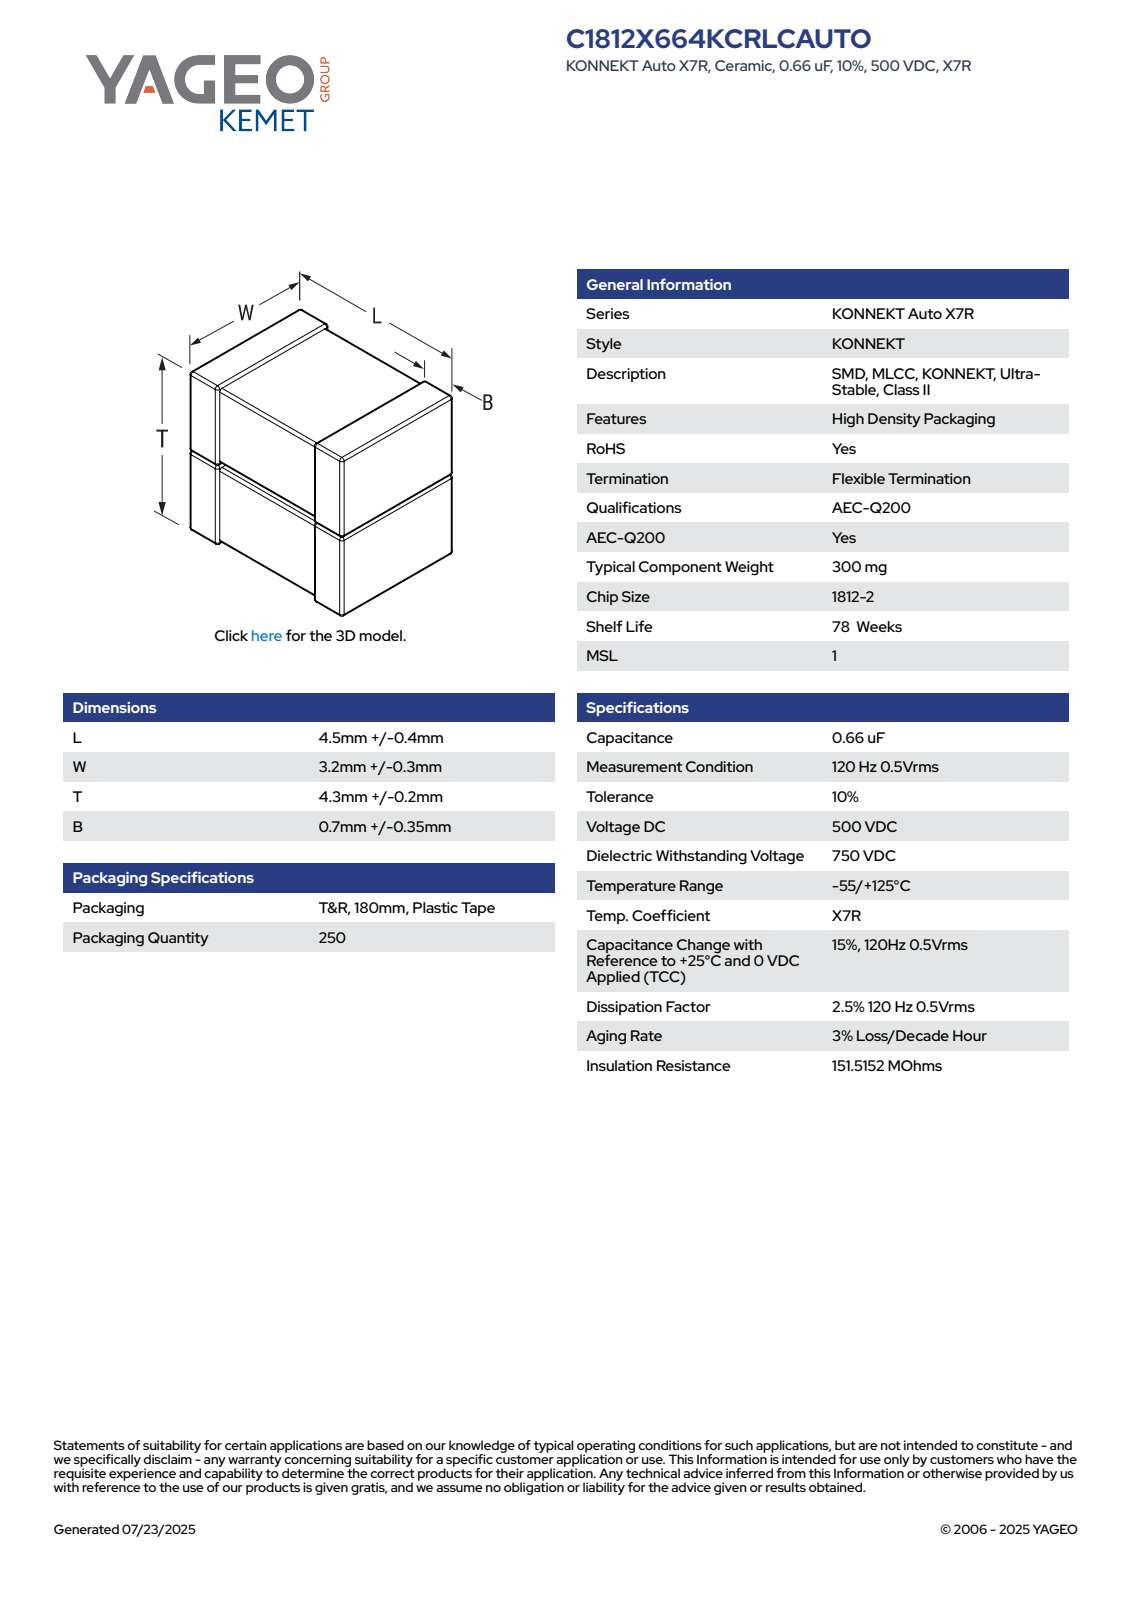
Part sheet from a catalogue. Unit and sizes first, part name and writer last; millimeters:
Units: millimetres
Overall size (bounding box): 4.9 × 4.5 × 3.5
Main face-to-face distances: 2.11, 2.25, 3.43, 4.9, 2.32, 2.18, 4.43, 3.36, 4.36, 3.5
Volume: 73 mm³ · Surface area: 129 mm²
Bodies: 4 solids, 197 faces (81 planar, 84 cylindrical, 32 other)
Part name (STEP PRODUCT): CCSS_K2T_1812-2_L4.9W3.5B1.05T4.5
STEP written by: SolidWorks 2020 (AUTOMOTIVE_DESIGN)
